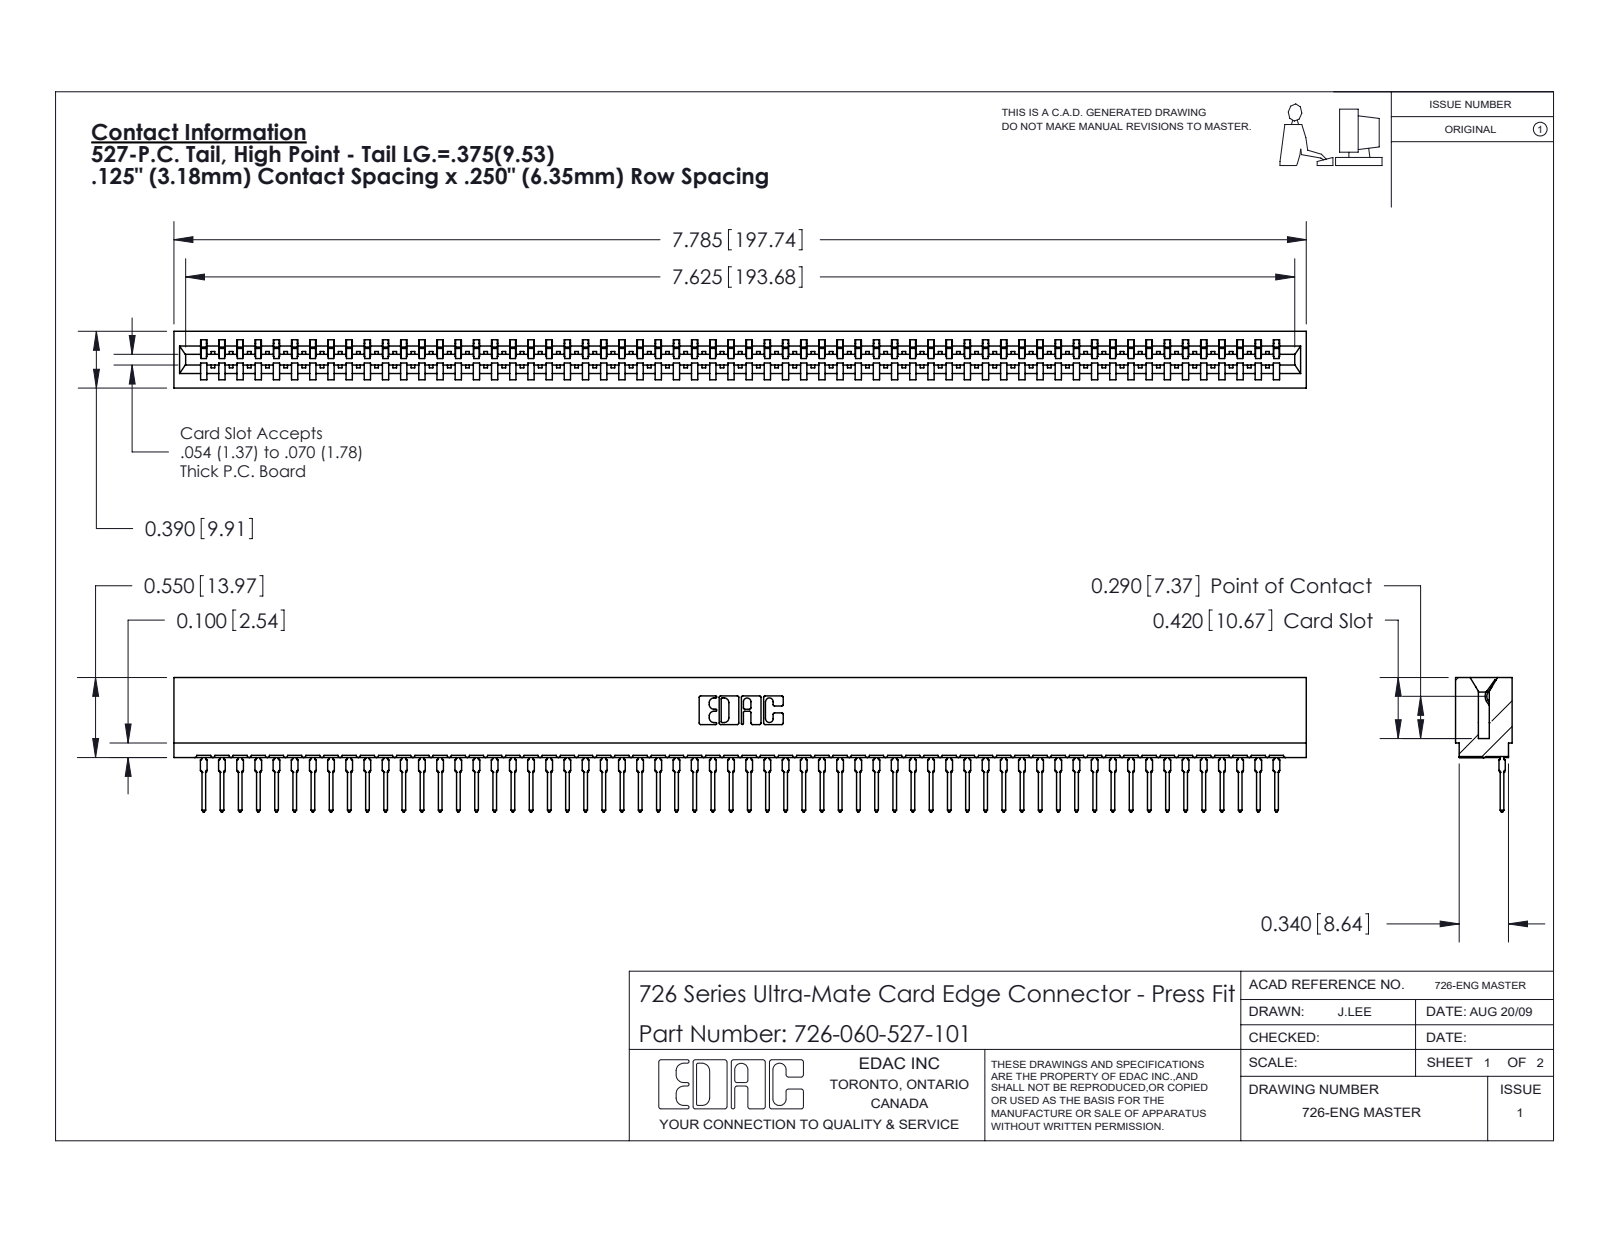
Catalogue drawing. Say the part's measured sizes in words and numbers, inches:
The part is named "726-060-527-101; 726 Part_.515 Slot Depth - 01; 746-292-001_527". Its 3-D file was written by "SolidWorks 2020 (CONFIG_CONTROL_DESIGN)". It is 61 solids with 6577 faces: 3835 planar, 1182 cylindrical and 1560 other. Overall it measures 7.785 by 0.924 by 0.39 inches. Its volume is 1.075 cubic inches and its surface area 42.6 square inches. Partial cylindrical surfaces (rounded edges, fillets, slot ends): 120 of radius 0.021, 61 of radius 0.015, 22 of radius 0.01, 6 of radius 0.007, 6 of radius 0.031, 4 of radius 0.005, 4 of radius 0.011, 3 of radius 0.026. The main face-to-face distances are 0.057, 0.333, 0.39, 0.025, 0.307, 0.25, 0.275, 0.083, 0.365, 0.032.
